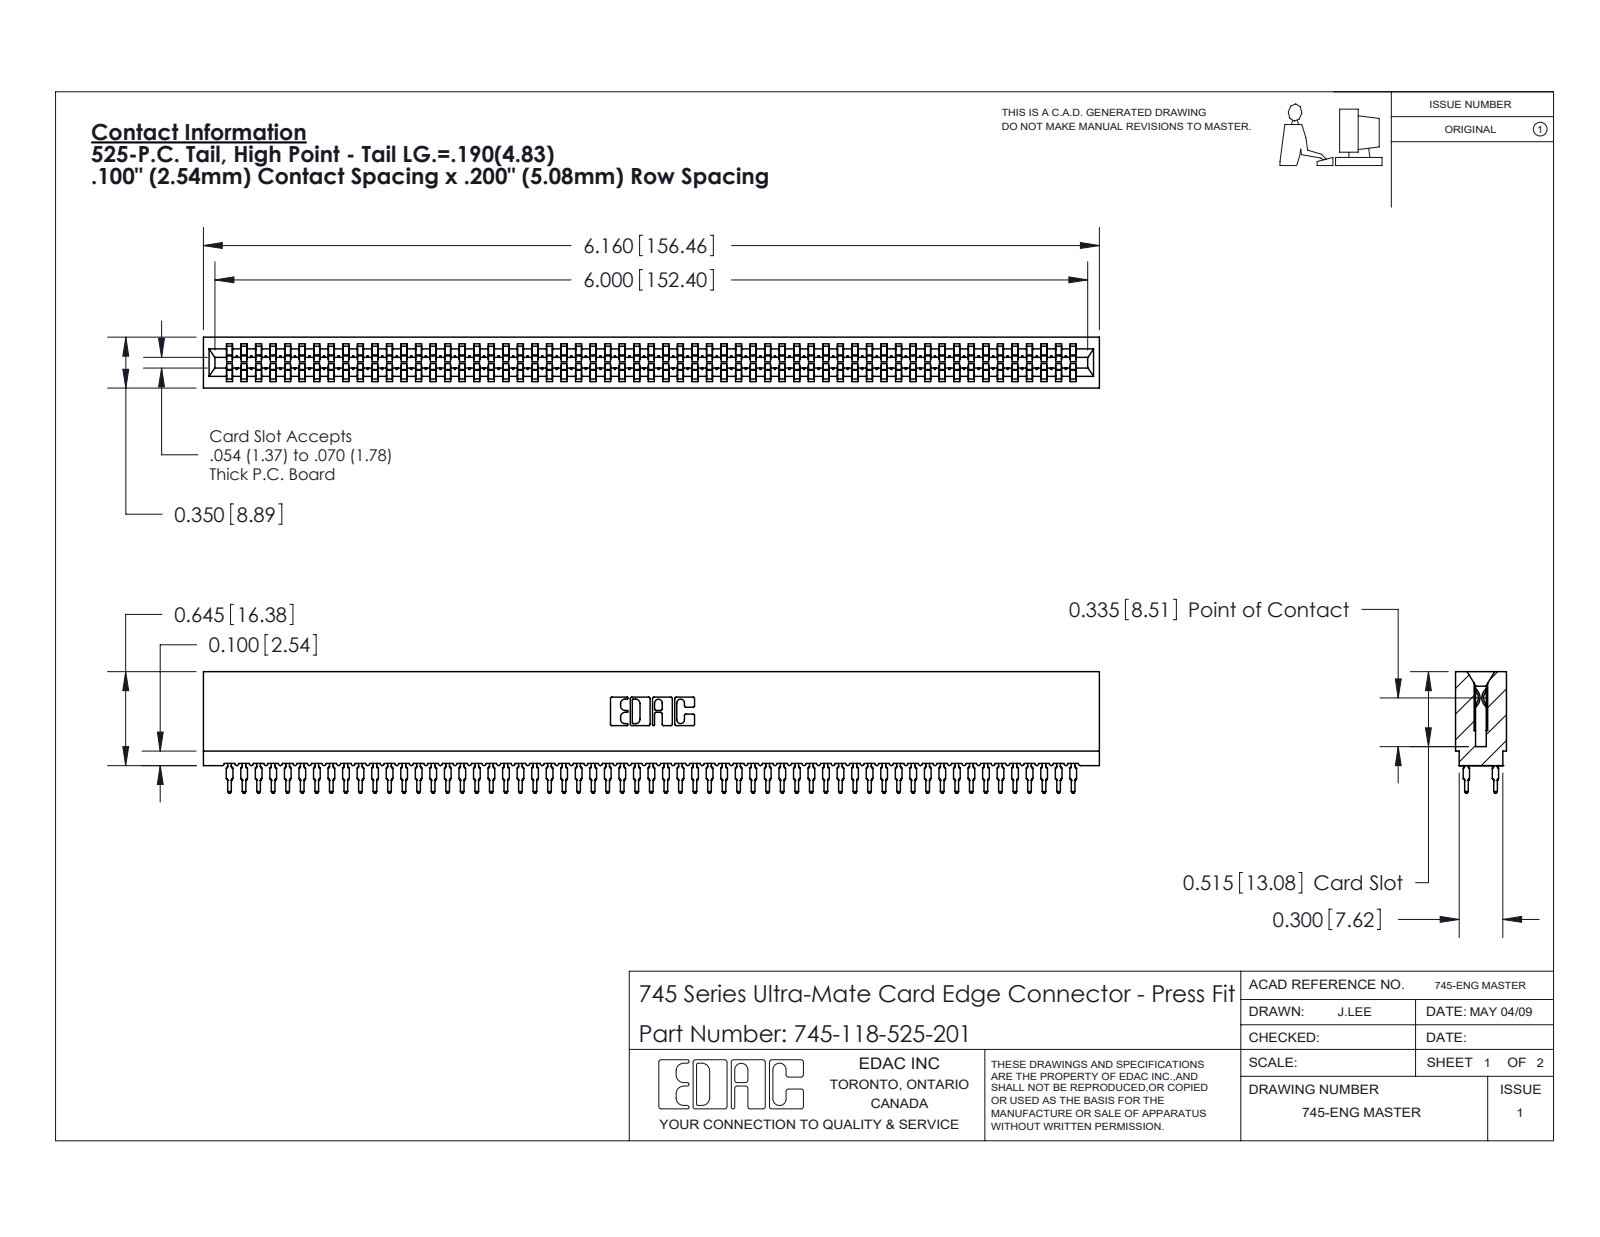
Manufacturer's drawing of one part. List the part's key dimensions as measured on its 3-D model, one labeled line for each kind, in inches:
Part name (STEP PRODUCT): 745 Part_Insulator Option - 01; 745-118-525-201; 745-292-001_525
STEP written by: SolidWorks 2020 (CONFIG_CONTROL_DESIGN)
Units: inches
Bodies: 119 solids, 10656 faces (5483 planar, 2105 cylindrical, 3068 other)
Overall size (bounding box): 6.16 × 0.836 × 0.35
Volume: 0.852 in³ · Surface area: 44.42 in²
Partial cylindrical surfaces — rounded edges, fillets, slot ends (radius × count): R0.021 ×236, R0.015 ×118, R0.01 ×22, R0.005 ×8, R0.011 ×8, R0.007 ×6, R0.031 ×6, R0.026 ×3
Main face-to-face distances: 0.35, 0.063, 0.287, 0.045, 0.305, 0.018, 0.243, 0.138, 0.212, 0.093
